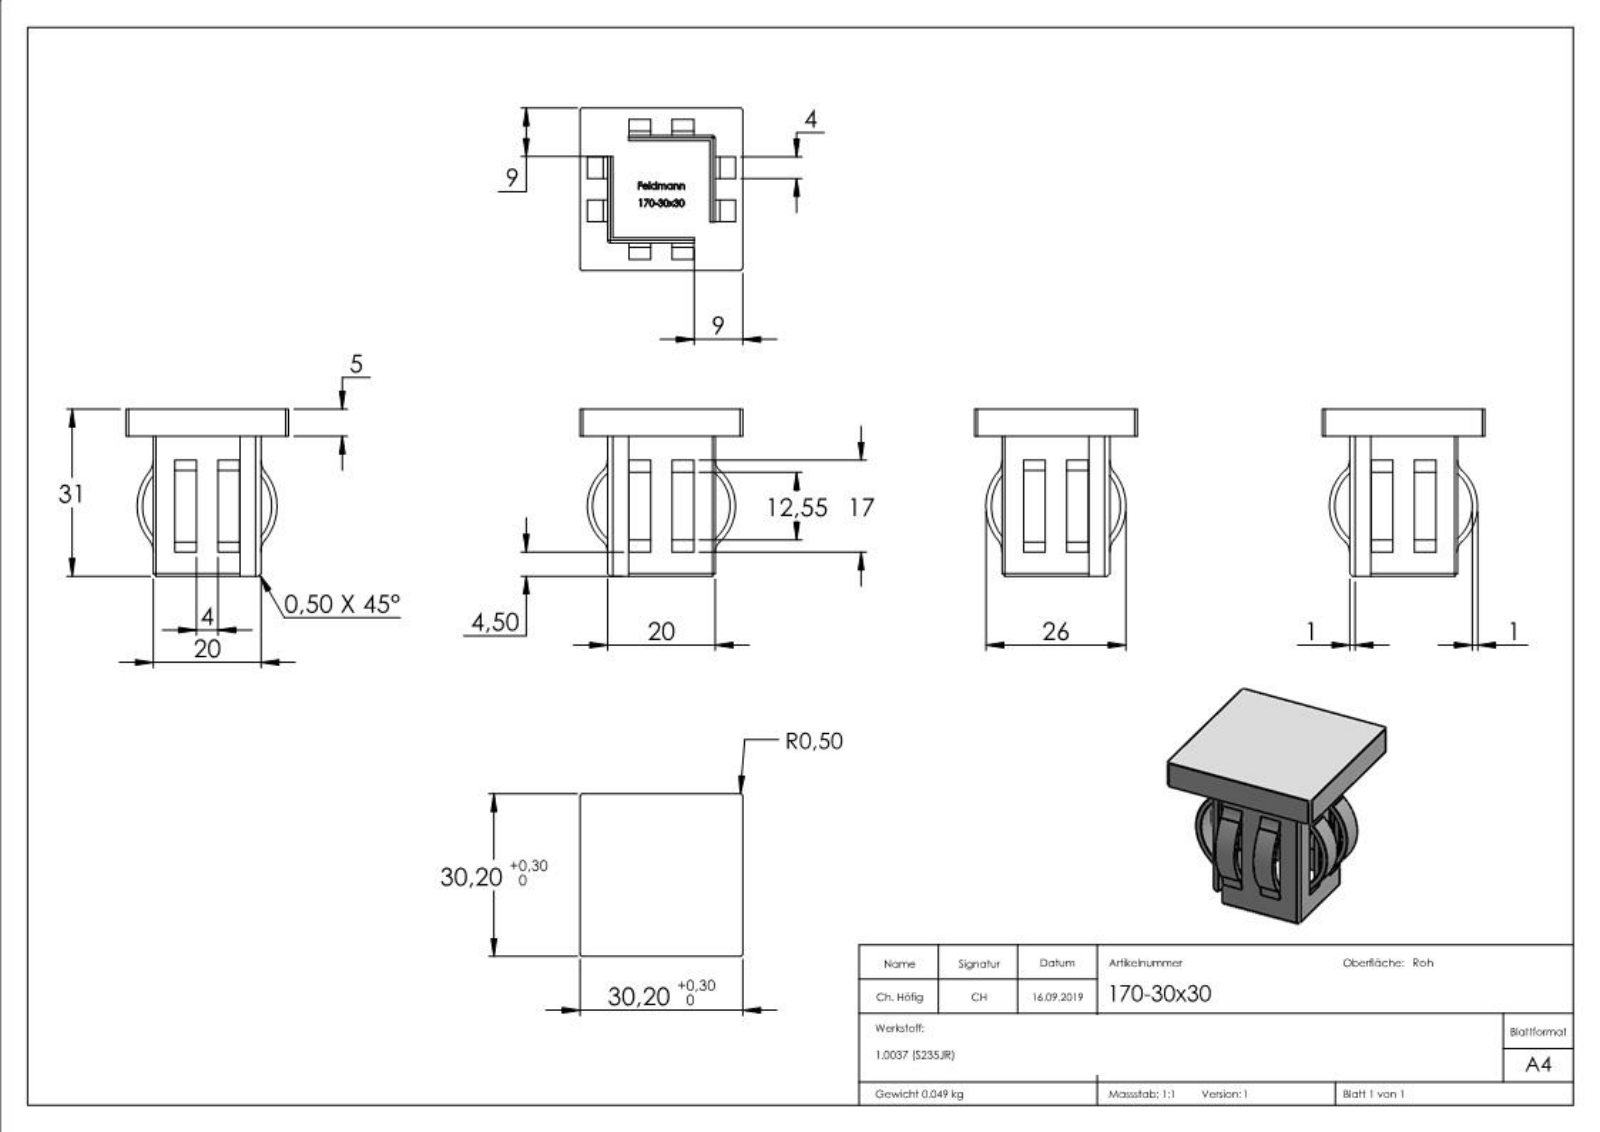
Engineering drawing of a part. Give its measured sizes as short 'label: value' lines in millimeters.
name: 170-30X30
written by: SolidWorks 2018 (CONFIG_CONTROL_DESIGN)
unit: mm
bodies: 1 solid, 318 faces (159 planar, 54 cylindrical, 105 other)
size: 31 × 30 × 30
volume: 6 738 mm³; area: 6 244 mm²
rounds: 8× R2, 8× R3.5, 6× R0.5, 4× R6.38, 4× R7.38
face distances: 5, 1.5, 18.5, 6.5, 17, 4, 23.5, 25, 20, 8
